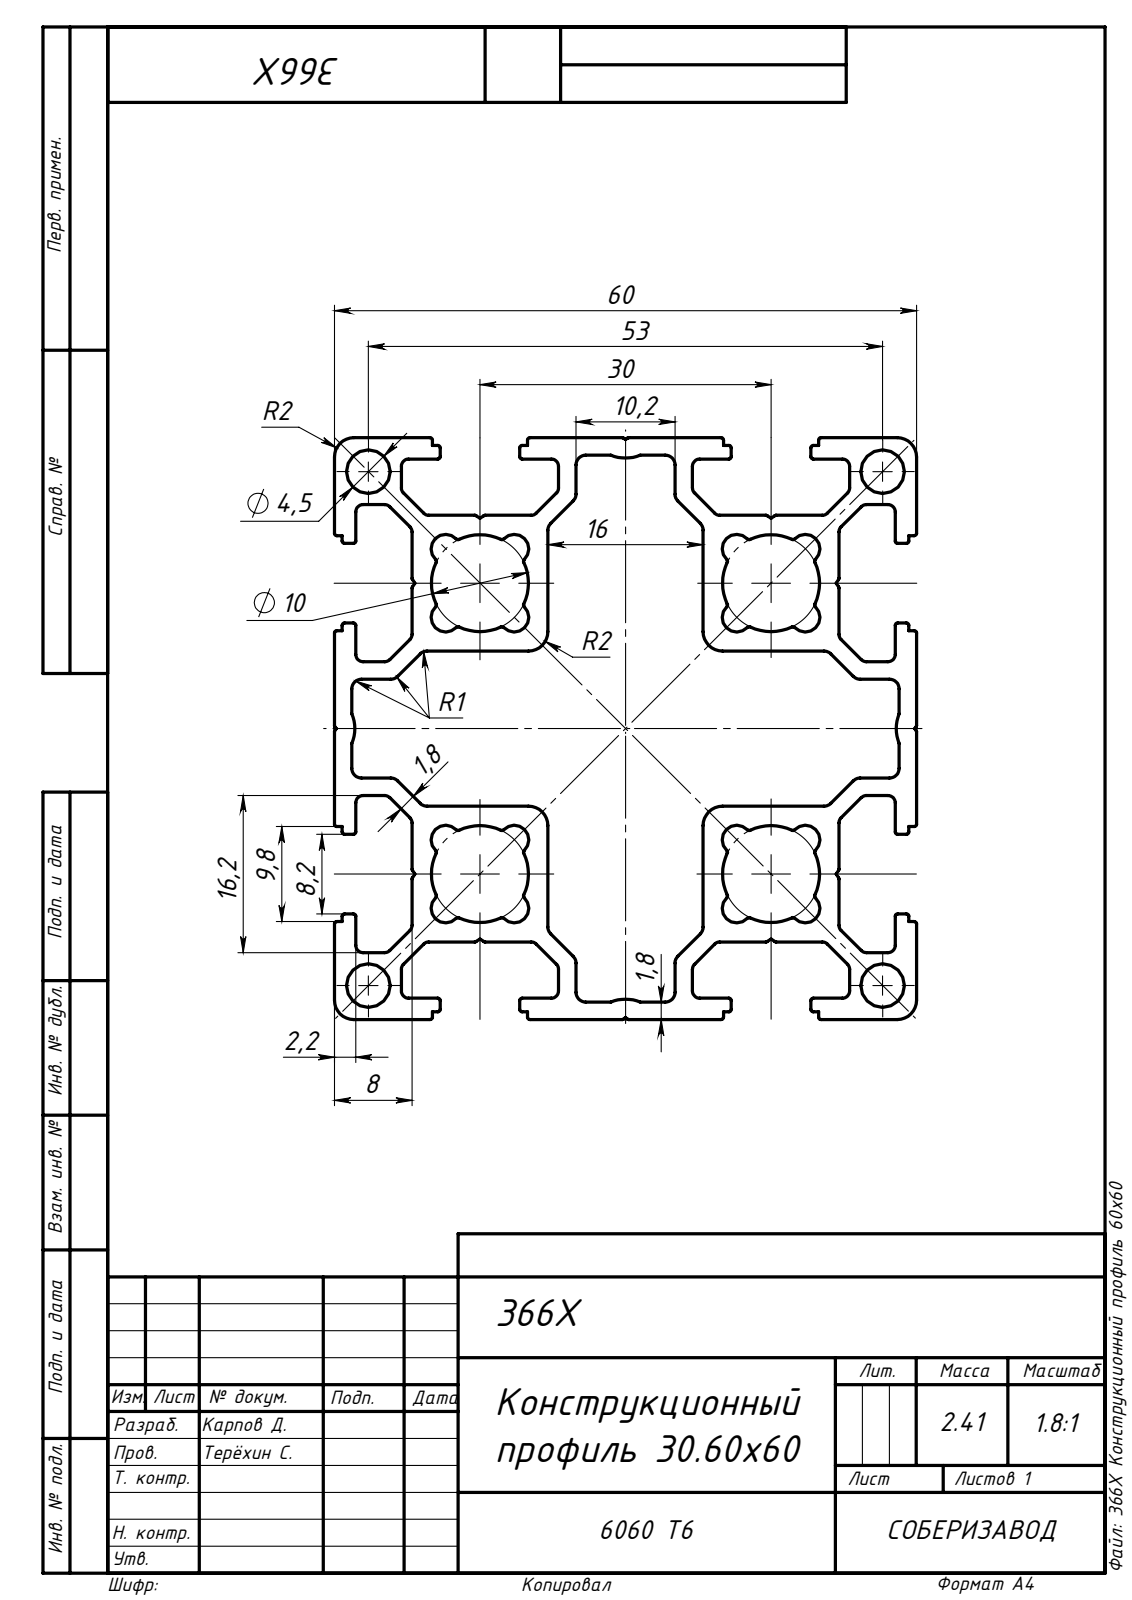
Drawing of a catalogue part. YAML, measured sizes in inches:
part_name: "366X Конструкционный профиль 60х60"
step_written_by: "SolidWorks 2019 (AUTOMOTIVE_DESIGN)"
units: inches
bodies: {solids: 1, faces: 434, planar: 186, cylindrical: 248, other: 0}
overall_size: [39.37, 2.362, 2.362]
volume: 54.4
surface_area: 1365
round_holes:
  - {diameter: 0.177, count: 4}
partial_cylinders:
  - {radius: 0.01, count: 104}
  - {radius: 0.03, count: 48}
  - {radius: 0.039, count: 24}
  - {radius: 0.059, count: 16}
  - {radius: 0.079, count: 8}
  - {radius: 0.157, count: 4}
  - {radius: 0.197, count: 4}
face_to_face_distances: [1.181, 0.866, 1.496, 0.551, 0.315, 2.047, 2.362, 0.071, 0.228, 0.087]
hole_center_spacings: [2.087, 2.951]
